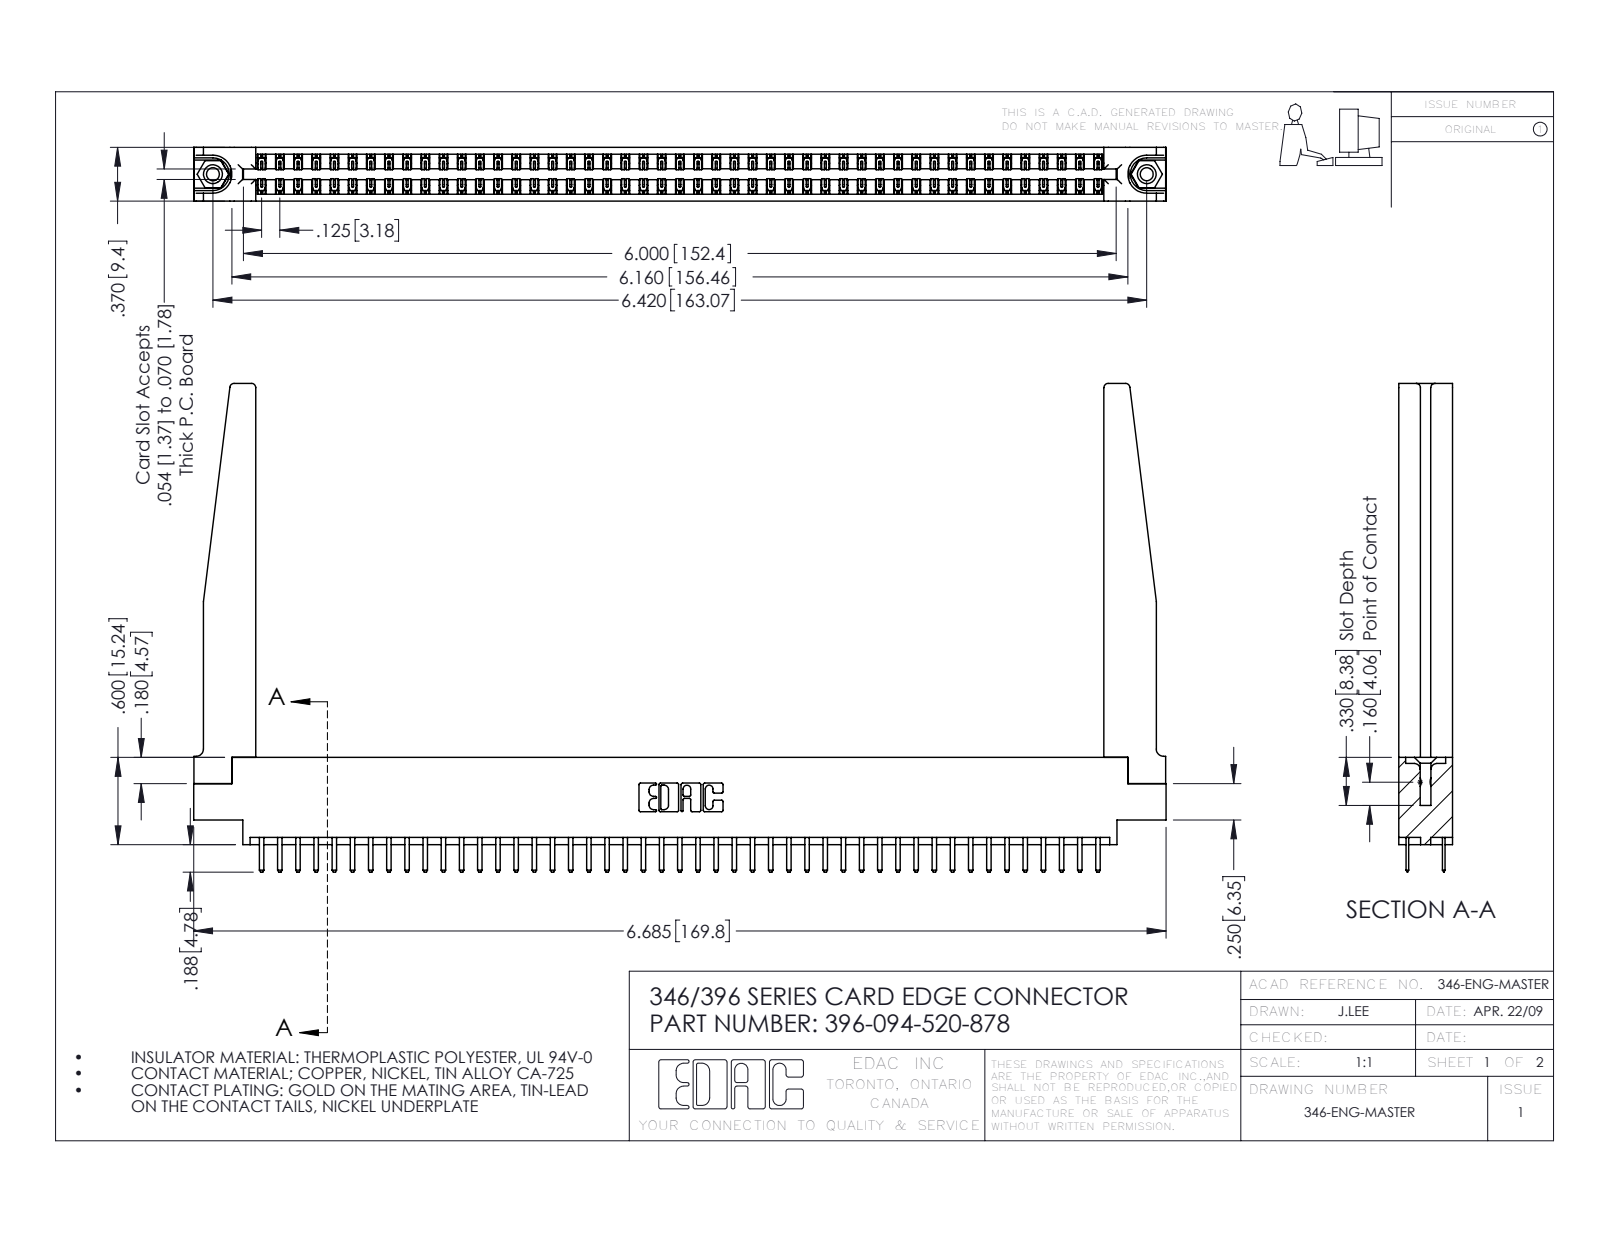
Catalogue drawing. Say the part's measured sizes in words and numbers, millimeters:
The part is named "346-220-078_345-220-078; 345-250-001_345-250-001-102; 346 Part_0.170 Offset - 0.156 Dia-TH; 345-292-001_345-293-120 (+1 more)". Its 3-D file was written by "SolidWorks 2016 (CONFIG_CONTROL_DESIGN)". It is 99 solids with 5624 faces: 3700 planar, 1872 cylindrical and 52 other. Overall it measures 169.8 by 85.3 by 9.4 millimeters. Its volume is 23 300 cubic millimeters and its surface area 29 250 square millimeters. Round holes: 2 of diameter 2.3, 2 of diameter 3.2, 2 of diameter 4, 1 of diameter 1.6. Round bosses or shafts: 2 of diameter 3.9. Partial cylindrical surfaces (rounded edges, fillets, slot ends): 141 of radius 0.2, 98 of radius 0.3, 22 of radius 0.3, 8 of radius 0.8, 6 of radius 0.2, 6 of radius 0.8, 3 of radius 0.7, 2 of radius 0.4. The main face-to-face distances are 9.4, 1.2, 8.2, 6.4, 1.8, 3.8, 3.8, 7.6, 0.6, 7. The hole center spacings are 6.2, 157.8, 163.1.
